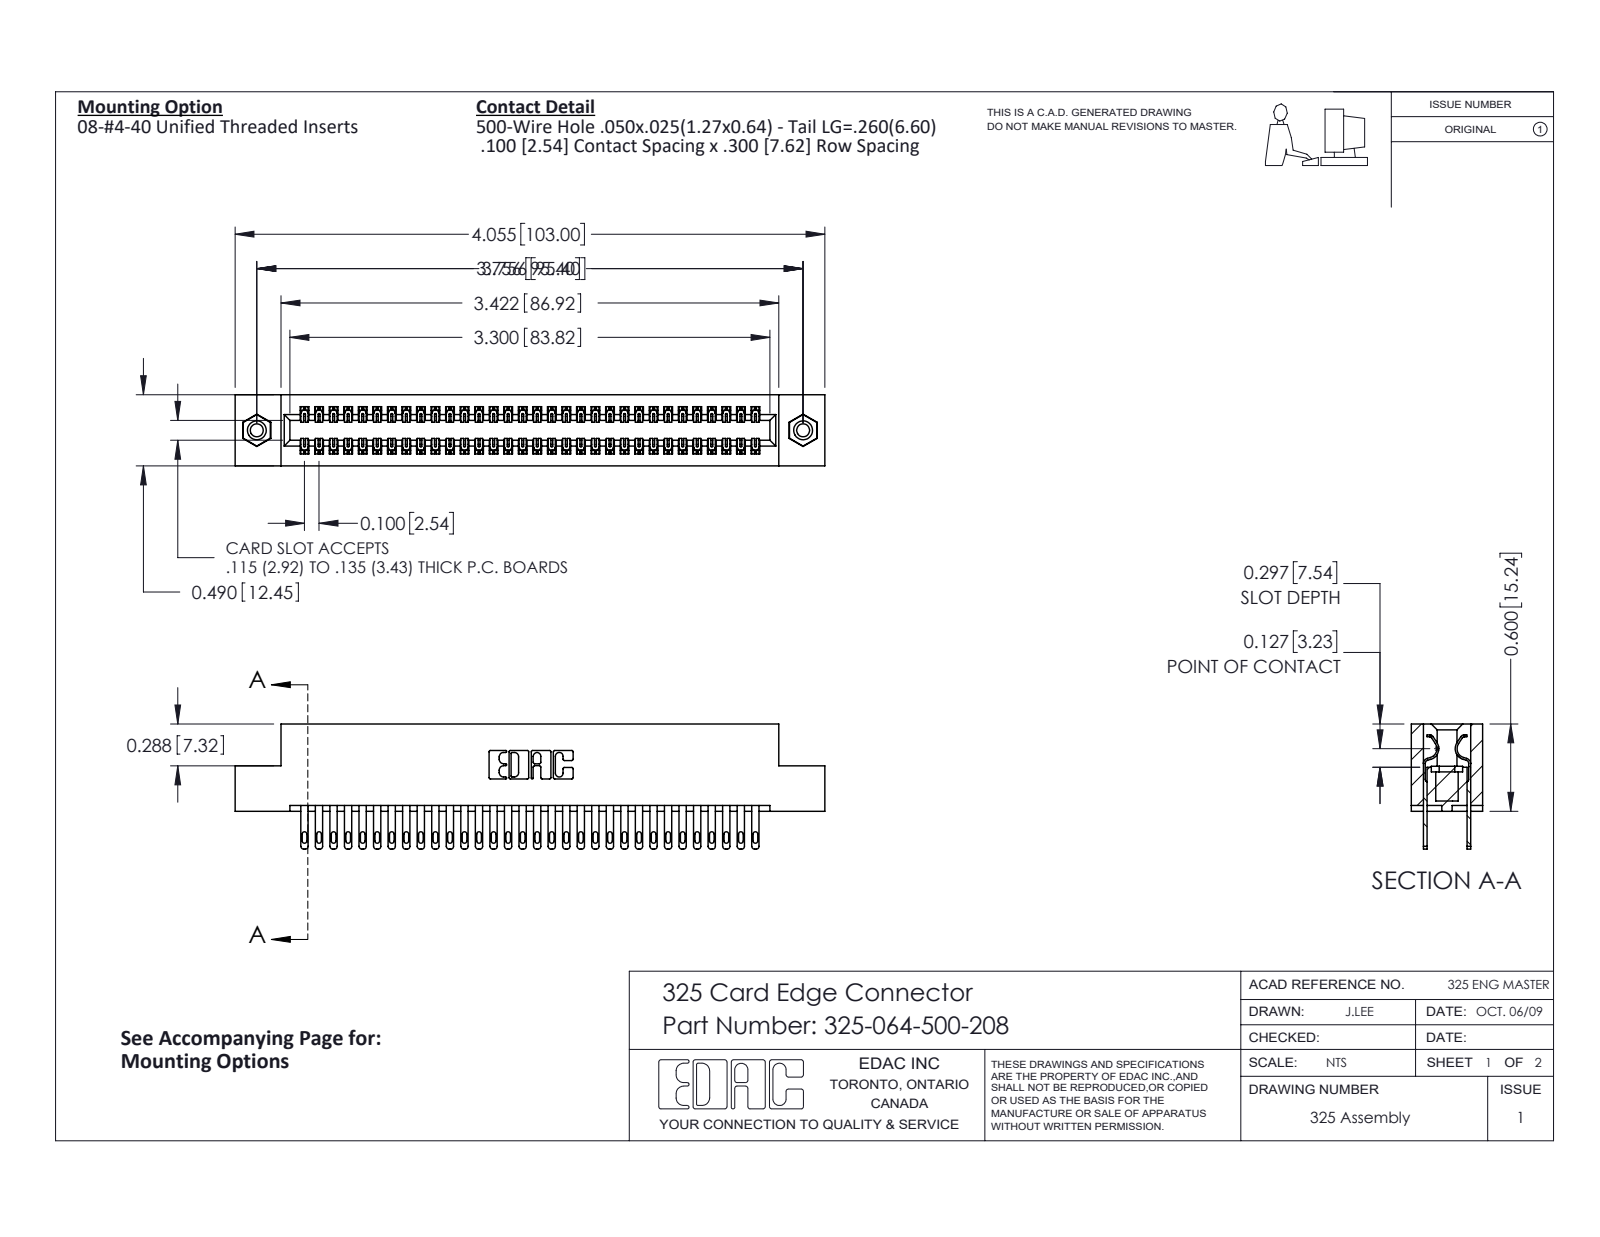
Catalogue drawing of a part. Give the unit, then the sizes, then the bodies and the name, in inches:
Units: inches
Overall size (bounding box): 4.055 × 0.86 × 0.49
Round holes (diameter × count): ⌀0.089 ×2, ⌀0.125 ×2, ⌀0.16 ×2
Round bosses / shafts (diameter × count): ⌀0.155 ×2
Partial cylindrical surfaces — rounded edges, fillets, slot ends (radius × count): R0.006 ×96, R0.016 ×64, R0.02 ×64, R0.01 ×22, R0.007 ×6, R0.031 ×6, R0.026 ×3, R0.014 ×2
Main face-to-face distances: 0.083, 0.407, 0.3, 0.107, 0.383, 0.025, 0.49, 0.325, 0.275, 0.04
Hole centre spacings: 3.756
Volume: 0.817 in³ · Surface area: 25.82 in²
Bodies: 67 solids, 3246 faces (2022 planar, 1208 cylindrical, 16 other)
Part name (STEP PRODUCT): 345-250-001_345-250-003-102; 325-292-001_325-293-100; 325 Part_TI; 325-064-500-208
STEP written by: SolidWorks 2016 (CONFIG_CONTROL_DESIGN)
